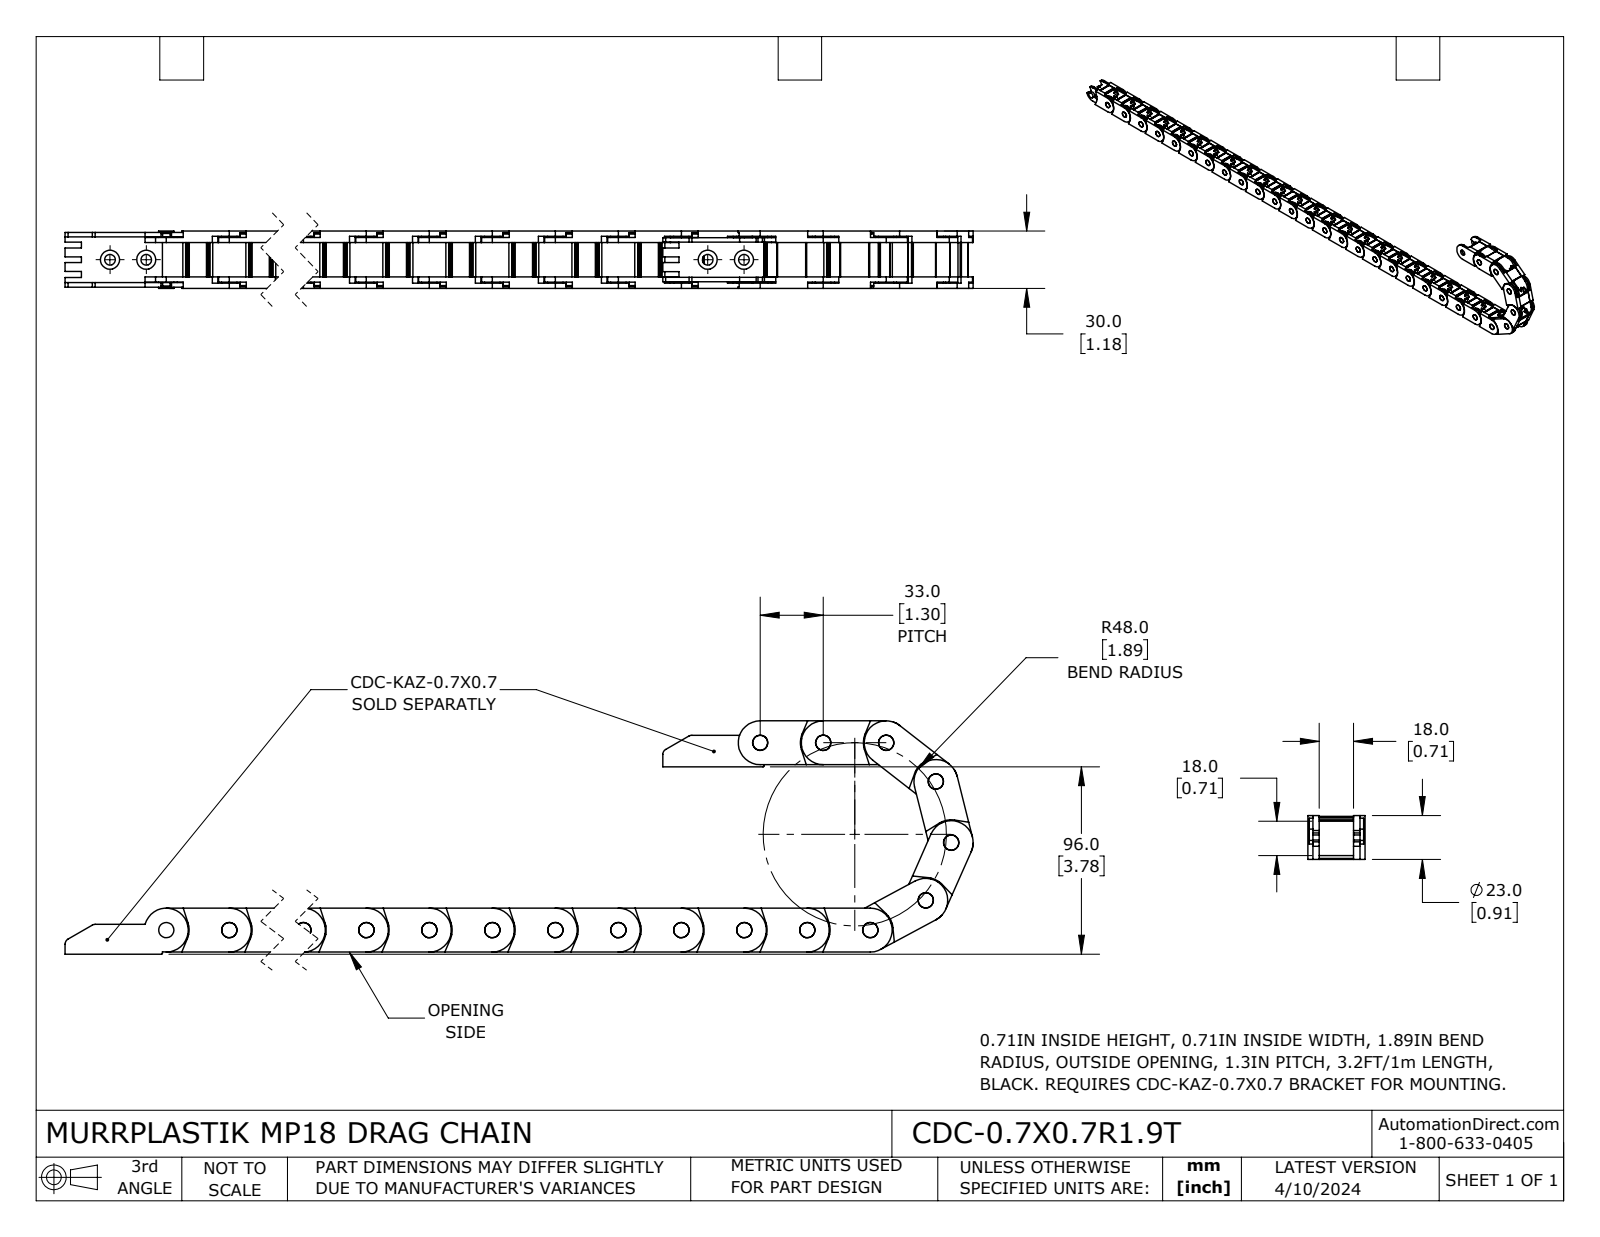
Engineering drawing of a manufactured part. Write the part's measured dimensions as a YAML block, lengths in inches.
part_name: "CDC-0.7X0.7R1.9T"
step_written_by: "SolidWorks 2023 (CONFIG_CONTROL_DESIGN)"
units: inches
bodies: {solids: 30, faces: 2730, planar: 1530, cylindrical: 1200, other: 0}
overall_size: [33.743, 4.767, 1.181]
volume: 16.11
surface_area: 321.6
round_holes:
  - {diameter: 0.315, count: 30}
round_bosses_or_shafts:
  - {diameter: 0.315, count: 1}
partial_cylinders:
  - {radius: 0.02, count: 120}
  - {radius: 0.059, count: 120}
  - {radius: 0.008, count: 60}
  - {radius: 0.012, count: 60}
  - {radius: 0.453, count: 31}
  - {radius: 0.47, count: 31}
  - {radius: 0.197, count: 30}
  - {radius: 0.215, count: 30}
face_to_face_distances: [0.945, 0.236, 0.106, 0.13, 1.181, 1.051, 0.815, 0.709, 1.075, 0.024]
hole_center_spacings: [1.299, 2.598, 3.898, 5.197, 6.496, 7.795, 9.094, 10.394]
